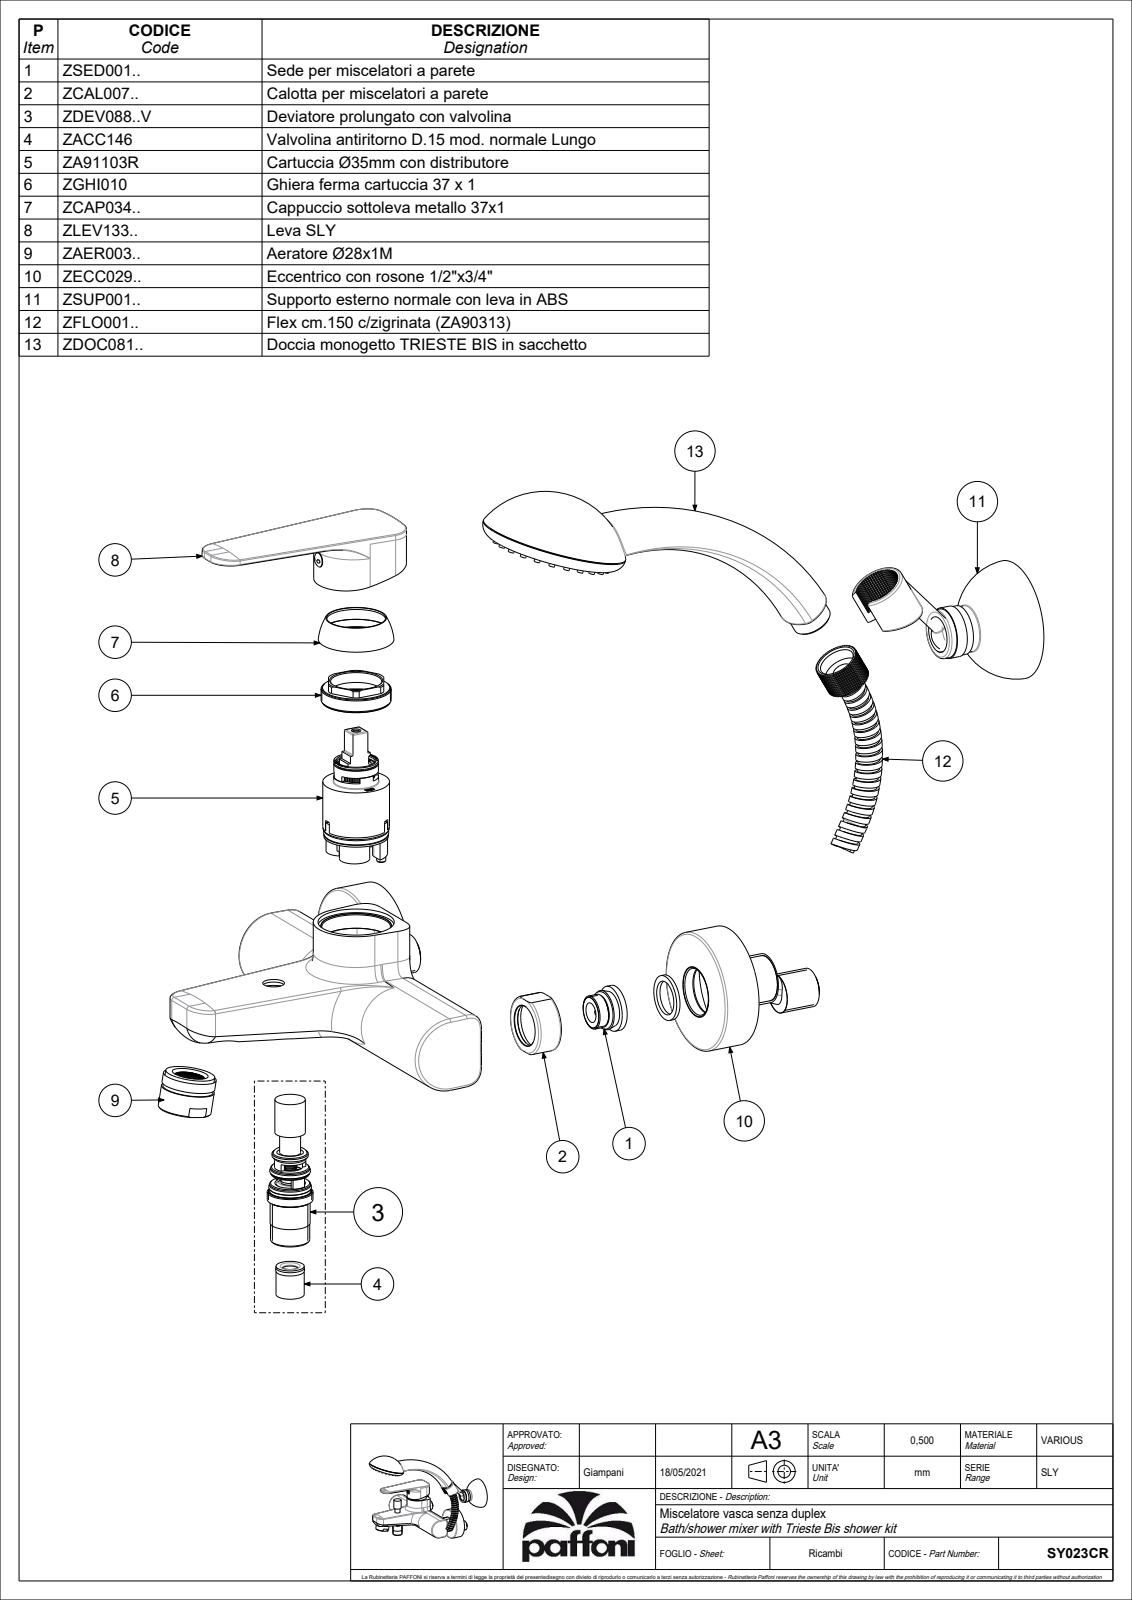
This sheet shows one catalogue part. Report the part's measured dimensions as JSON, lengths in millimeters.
{"part_name": "SY023CR", "step_written_by": "CREO PARAMETRIC BY PTC INC, 2020044 (CONFIG_CONTROL_DESIGN)", "units": "millimeters", "bodies": {"solids": 7, "faces": 3996, "planar": 2491, "cylindrical": 600, "other": 905}, "overall_size": [321.98, 285.07, 264.67], "volume_mm3": 411922, "surface_area_mm2": 246343, "round_holes": [[12, 4], [19, 4], [9, 3], [24.5, 3], [25, 3], [3.3, 2], [4, 2], [5, 2], [8, 2], [10, 2], [10.5, 2], [16.5, 2]], "round_bosses_or_shafts": [[24, 3], [63.5, 2], [27, 2], [20.6, 2], [10, 2], [75.5, 1], [72.5, 1], [65.8, 1]], "partial_cylinders_radius": [[0.5, 56], [0.75, 16], [0.15, 11], [0.3, 9], [1.5, 6], [1, 4], [7, 4], [4.5, 3]], "face_to_face_distances": [3.5, 15, 0.6, 18.5, 3, 15.6, 26.5, 36.5, 19.1, 26], "hole_center_spacings": [0.71, 8.51, 8.6, 13.04, 13.21, 13.51, 44.97, 45.54]}
